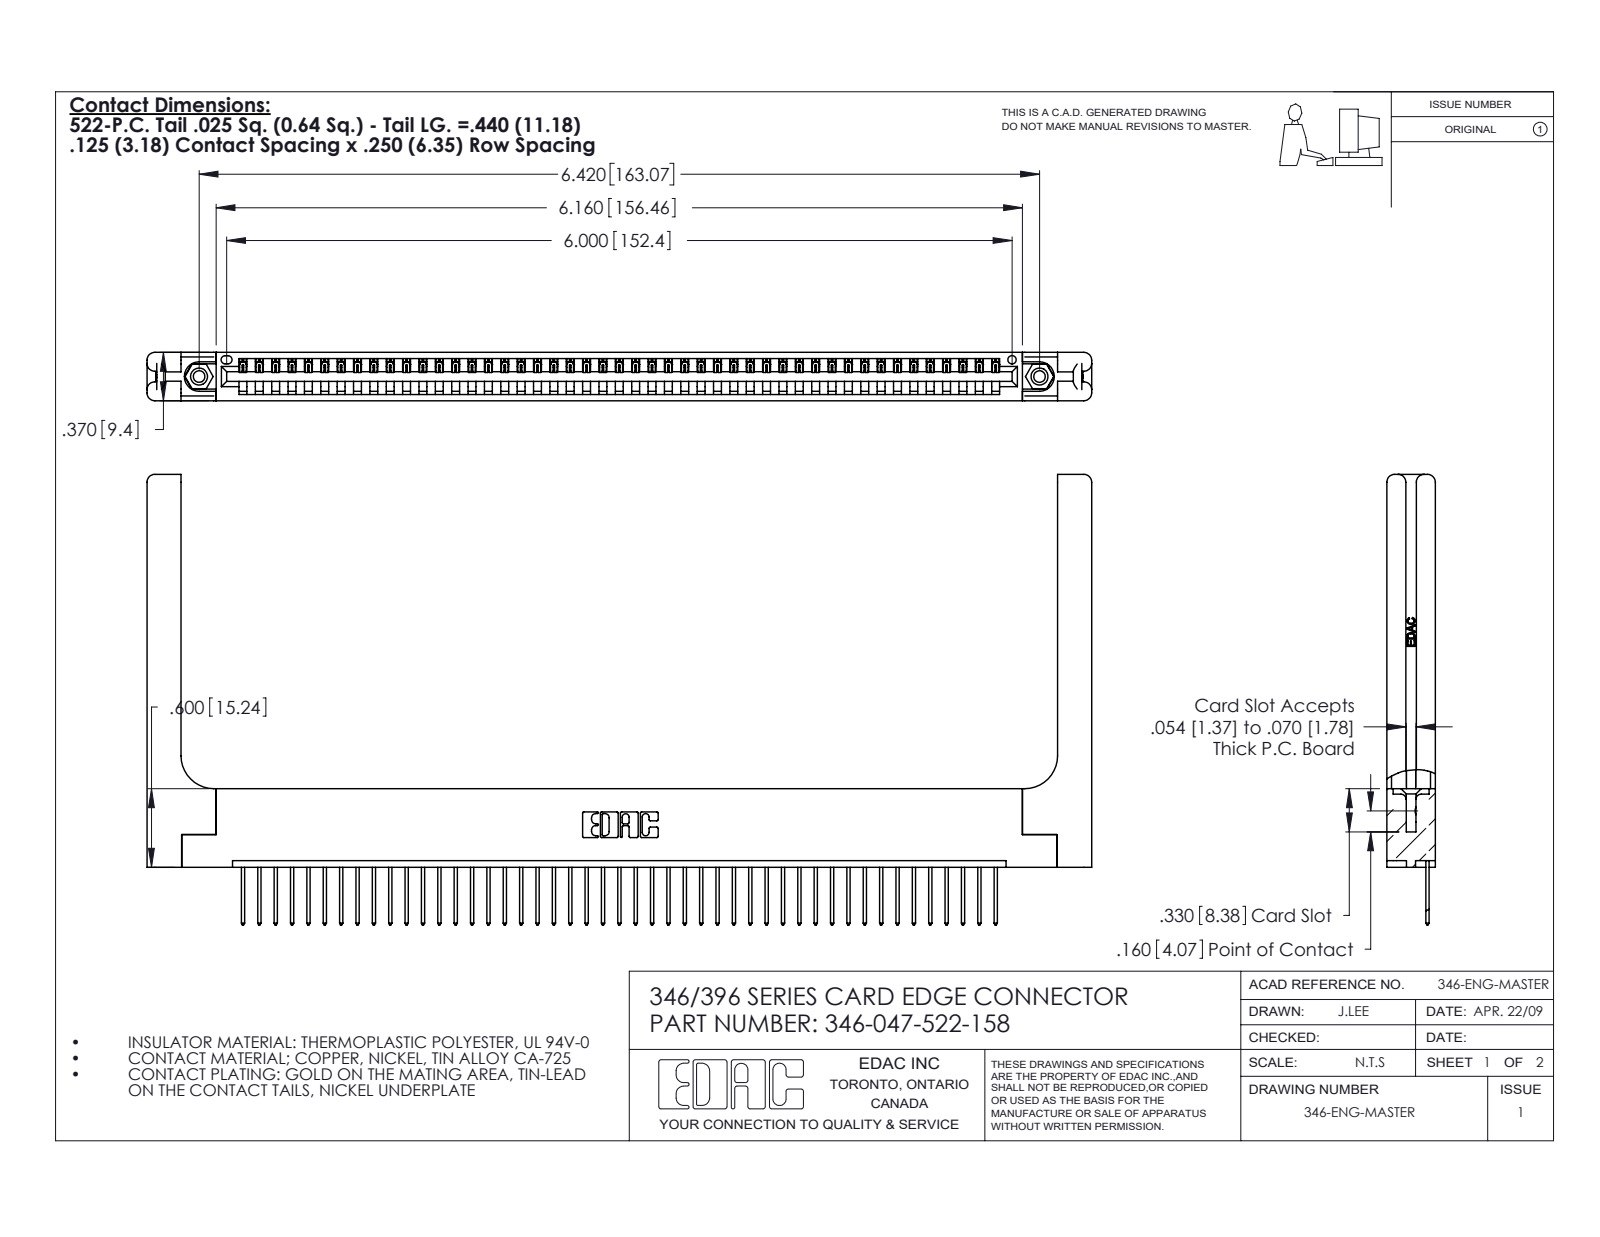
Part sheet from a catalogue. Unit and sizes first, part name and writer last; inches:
Units: inches
Overall size (bounding box): 7.216 × 3.44 × 0.37
Round holes (diameter × count): ⌀0.089 ×2, ⌀0.125 ×2, ⌀0.156 ×2, ⌀0.064 ×1
Round bosses / shafts (diameter × count): ⌀0.155 ×2
Partial cylindrical surfaces — rounded edges, fillets, slot ends (radius × count): R0.006 ×94, R0.01 ×94, R0.01 ×22, R0.06 ×16, R0.007 ×6, R0.031 ×6, R0.026 ×3, R0.03 ×2
Main face-to-face distances: 0.37, 0.048, 0.322, 0.072, 0.148, 0.15, 0.25, 0.298, 0.025, 0.222
Hole centre spacings: 0.246, 6.211, 6.42
Volume: 1.531 in³ · Surface area: 42.45 in²
Bodies: 52 solids, 3118 faces (2118 planar, 940 cylindrical, 60 other)
Part name (STEP PRODUCT): 345-292-001_345-293-122; 346-220-058_345-220-058; 346 Part_Flush Mounting Lugs - 0.156 Dia-TH; 346-047-522-158 (+1 more)
STEP written by: SolidWorks 2020 (CONFIG_CONTROL_DESIGN)
